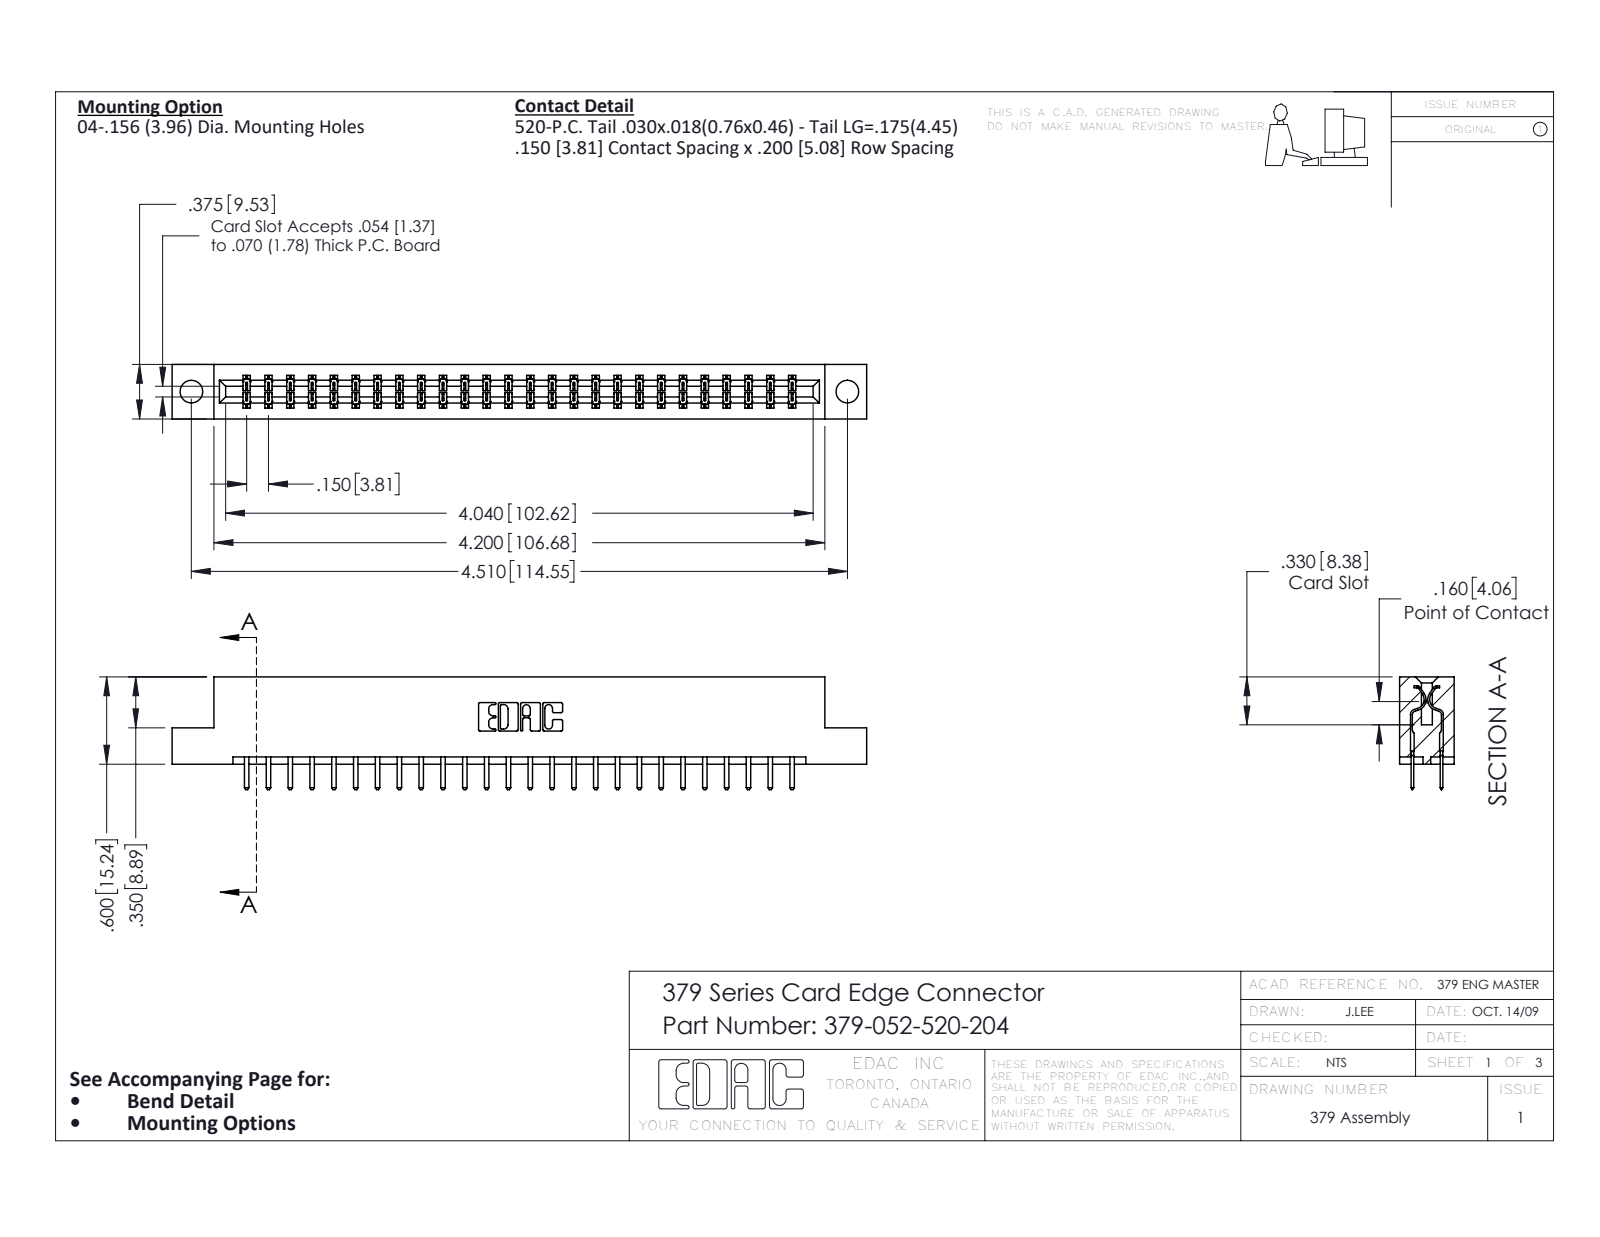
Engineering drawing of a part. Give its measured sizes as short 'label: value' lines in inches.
name: 379-052-520-204; 345-292-001_345-293-120; 379 Part_Flush - .156 Dia - TH
written by: SolidWorks 2016 (CONFIG_CONTROL_DESIGN)
unit: in
bodies: 53 solids, 3026 faces (2046 planar, 980 cylindrical, 0 other)
size: 4.775 × 0.775 × 0.375
volume: 0.77 in³; area: 21.31 in²
holes: 2× ⌀0.156
rounds: 78× R0.006, 56× R0.01, 22× R0.01, 6× R0.007, 6× R0.031, 3× R0.026, 2× R0.014, 2× R0.022
face distances: 0.3, 0.075, 0.375, 0.2, 0.225, 0.1, 0.55, 0.15, 0.076, 0.05
hole spacings: 4.51
